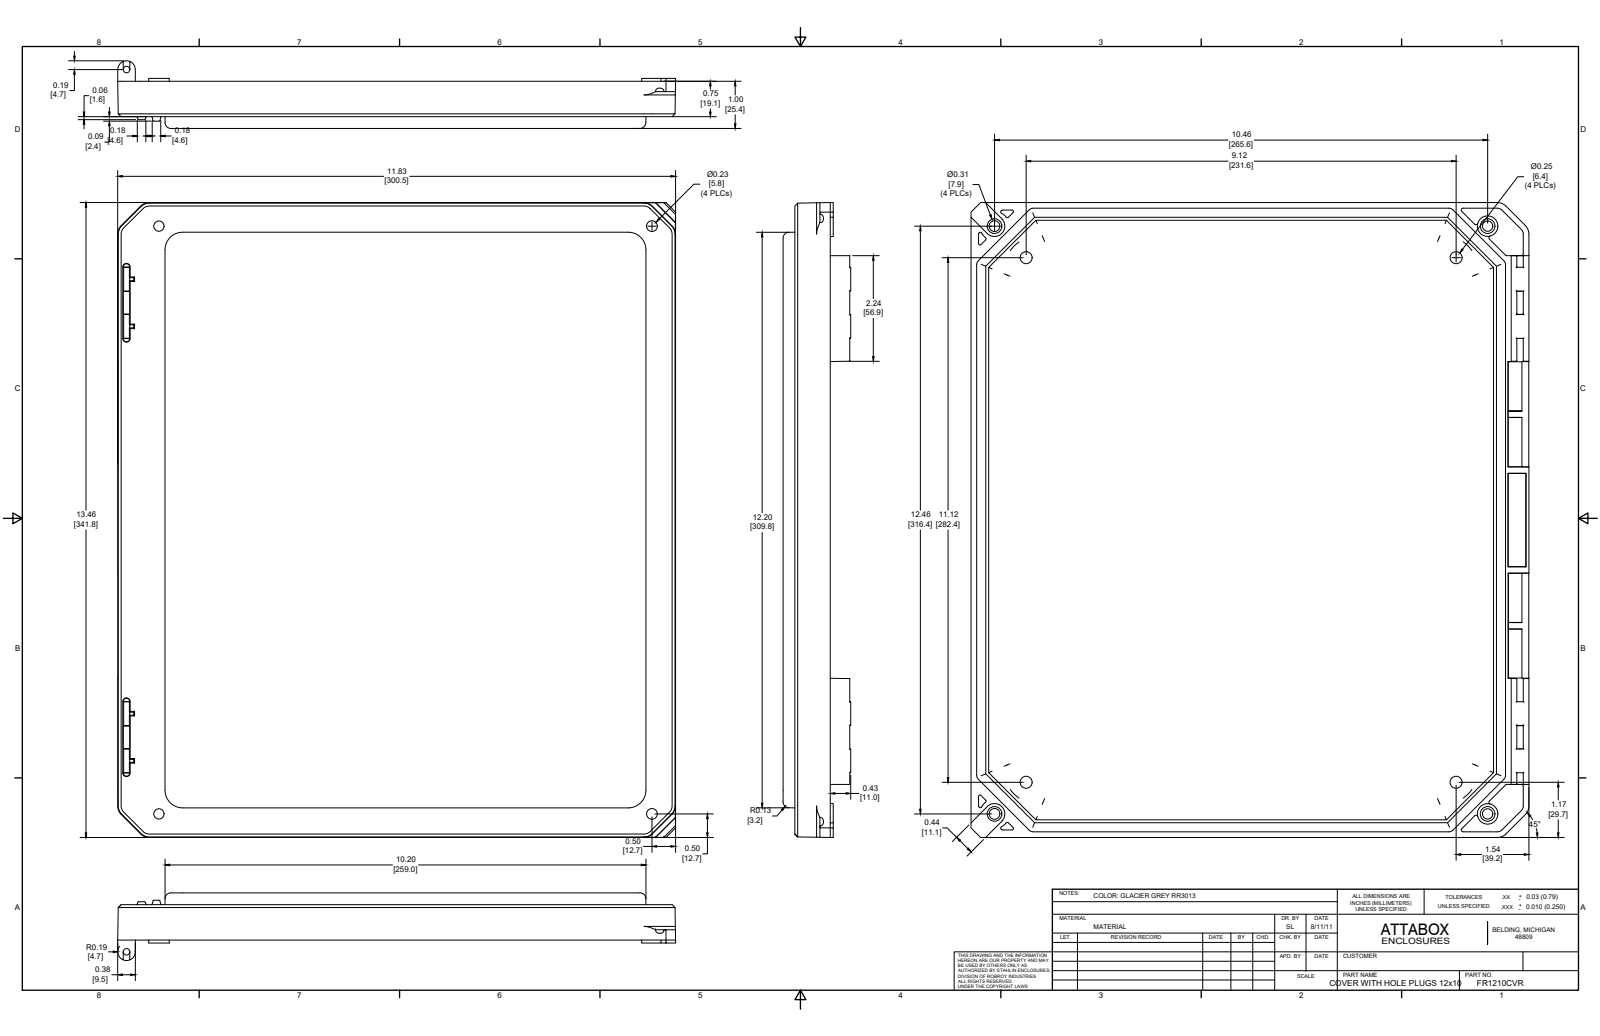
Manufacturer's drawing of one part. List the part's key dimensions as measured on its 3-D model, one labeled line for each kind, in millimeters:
Part name (STEP PRODUCT): FR1210CVR
STEP written by: SolidWorks 2019 (AUTOMOTIVE_DESIGN)
Units: millimetres
Bodies: 1 solid, 606 faces (264 planar, 194 cylindrical, 148 other)
Overall size (bounding box): 341.8 × 300.5 × 36.4
Volume: 570 800 mm³ · Surface area: 278 300 mm²
Round holes (diameter × count): ⌀6.4 ×4, ⌀5.6 ×2, ⌀5.8 ×2, ⌀8 ×2, ⌀3.5 ×1
Round bosses / shafts (diameter × count): ⌀11 ×1, ⌀11 ×1
Partial cylindrical surfaces — rounded edges, fillets, slot ends (radius × count): R0.8 ×27, R2.4 ×16, R1.6 ×15, R0.3 ×14, R3.2 ×12, R1.5 ×11, R1 ×10, R1.6 ×9
Main face-to-face distances: 3.2, 6.4, 3.2, 9.5, 19.1, 25.4, 22.2, 15.9, 9.5, 3.4
Hole centre spacings: 299.9, 24, 24.1, 231.6, 249.1, 249.2, 265.6, 282.4
